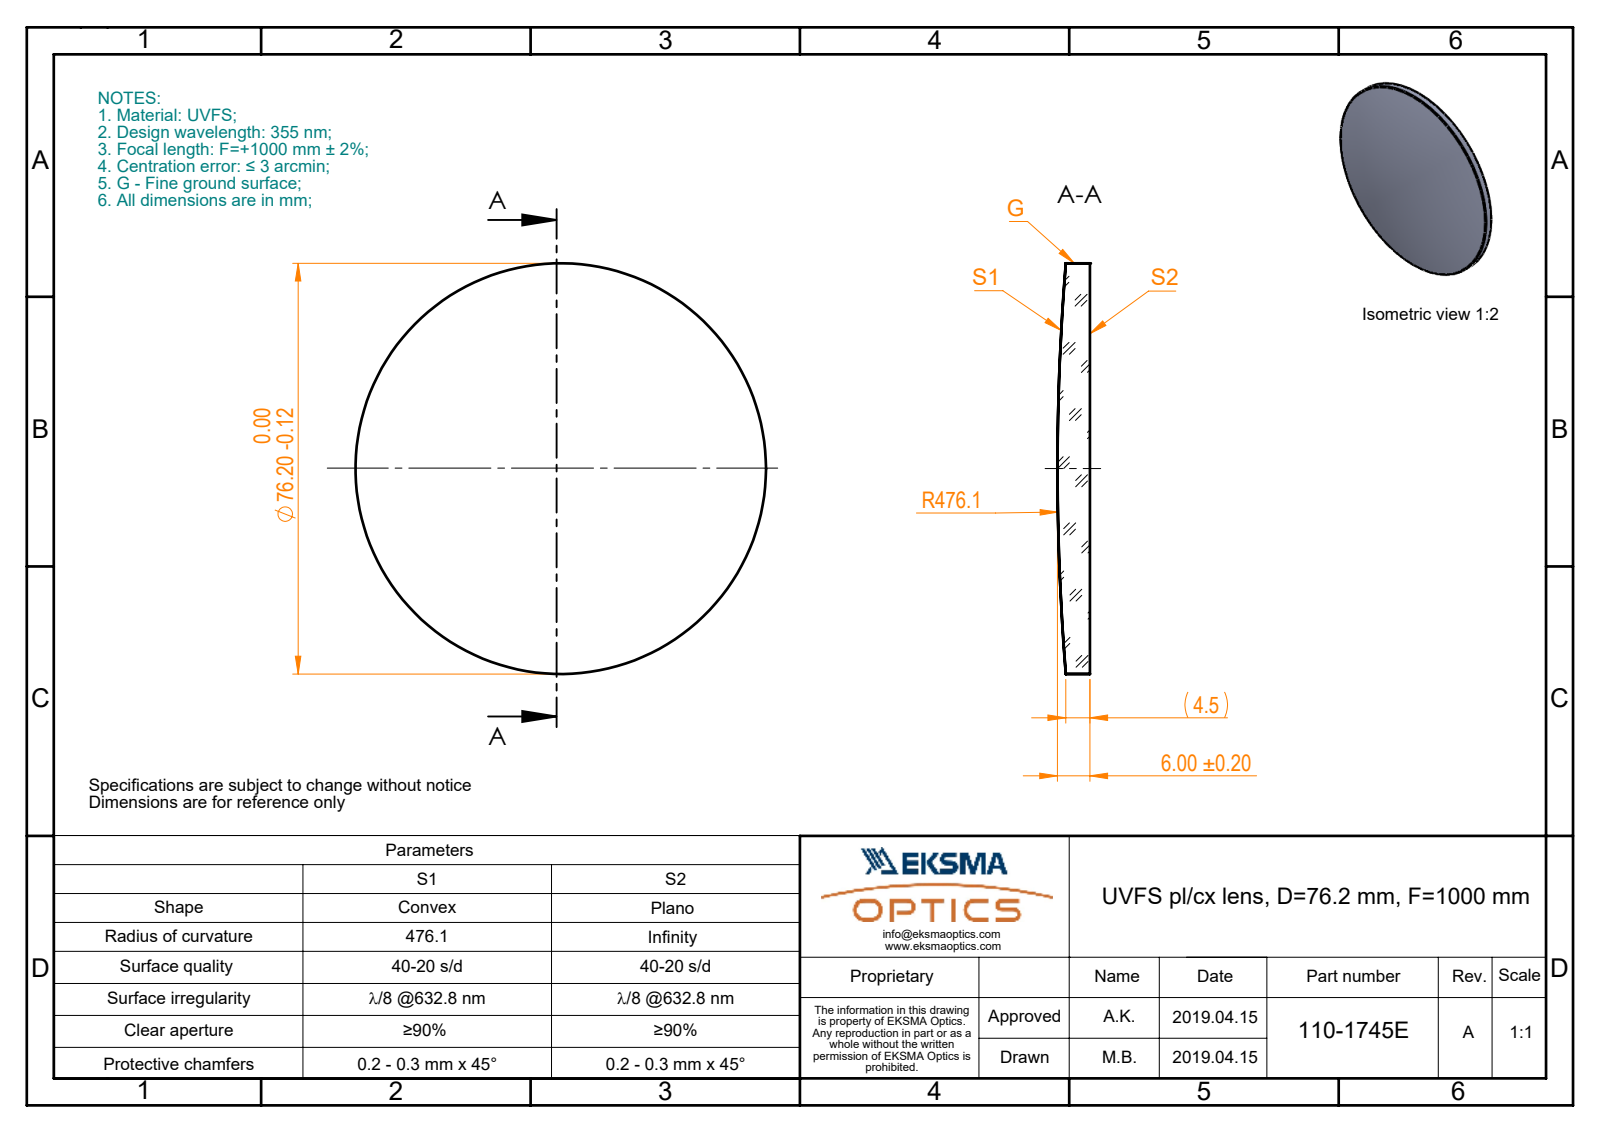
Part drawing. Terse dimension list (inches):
name: 110-1745E UVFS pl-cx 76.2 F1000
written by: SolidWorks 2017 (CONFIG_CONTROL_DESIGN)
unit: in
bodies: 1 solid, 5 faces (1 planar, 2 cylindrical, 2 other)
size: 3 × 3 × 0.236
volume: 1.457 in³; area: 15.81 in²
bosses: 1× ⌀3
